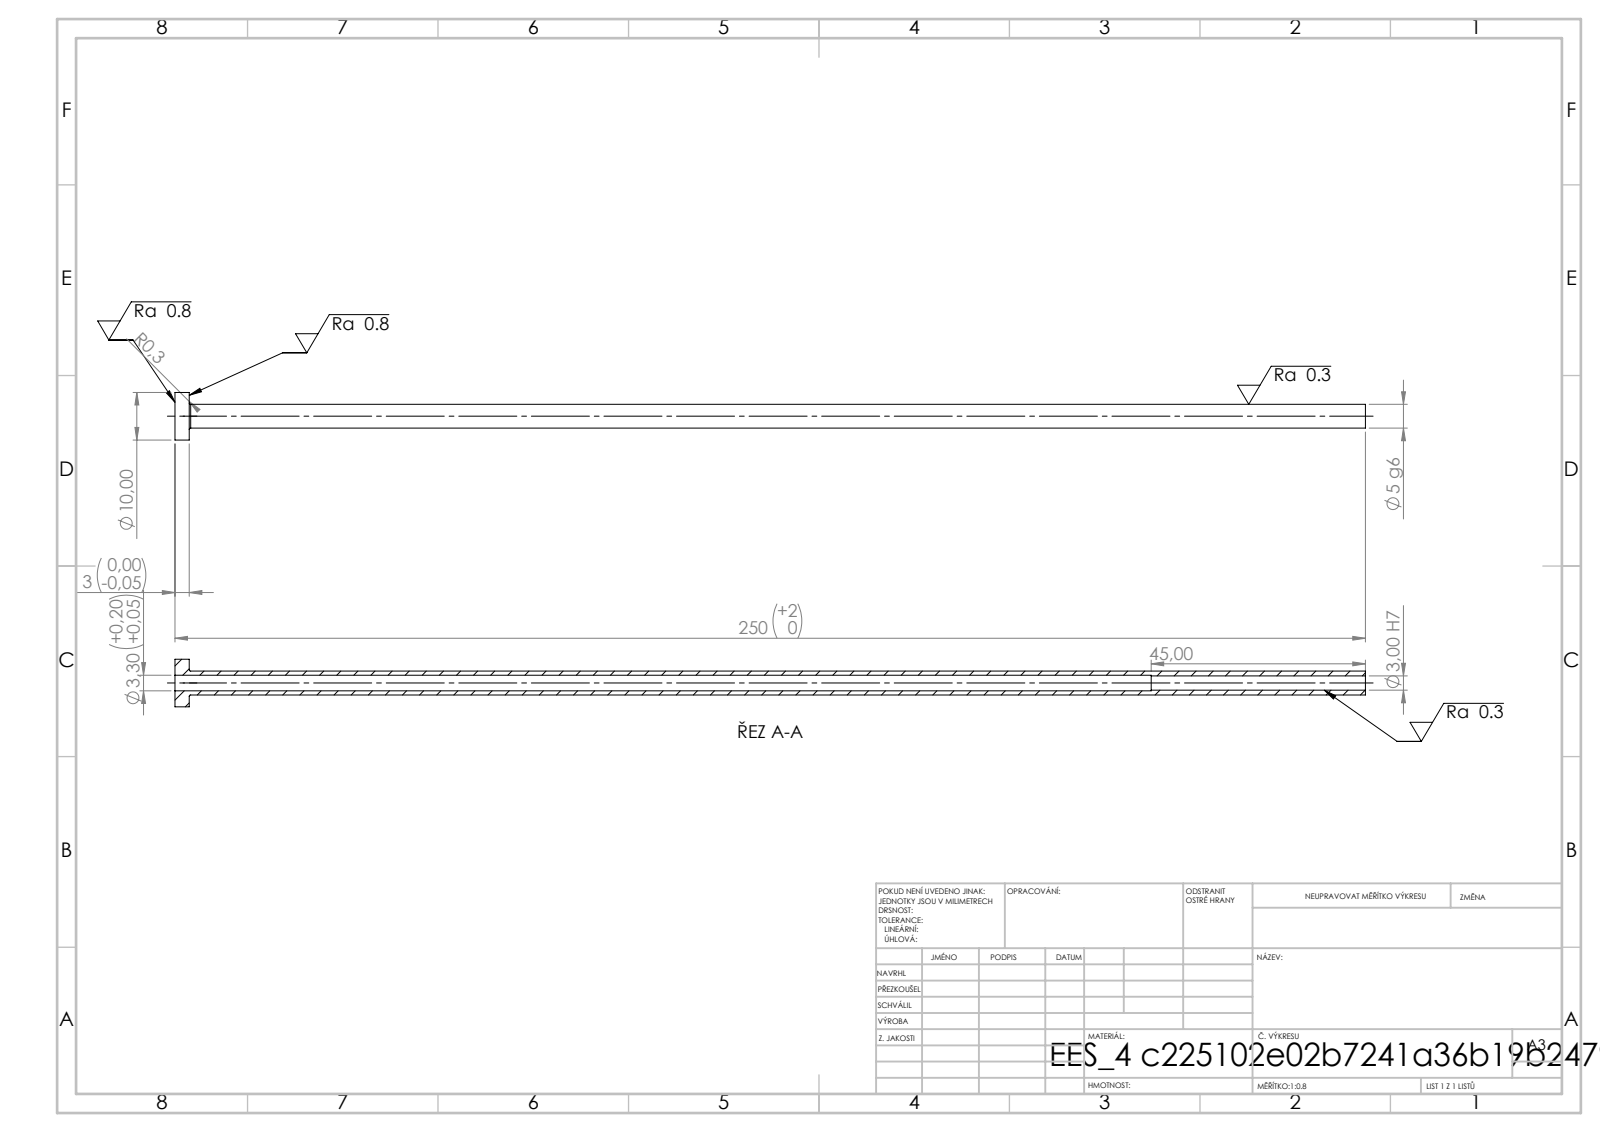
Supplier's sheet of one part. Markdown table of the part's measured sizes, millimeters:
| quantity | value |
| --- | --- |
| STEP written by | SolidWorks 2019 (CONFIG_CONTROL_DESIGN) |
| units | millimeters |
| bodies | 1 solid, 14 faces (4 planar, 8 cylindrical, 2 other) |
| overall size | 250 × 10 × 10 |
| volume | 3 014 mm³ |
| surface area | 6 664 mm² |
| round holes (diameter × count) | 3 × 1, 3.3 × 1 |
| round bosses / shafts (diameter × count) | 10 × 1, 5 × 1 |
| main face-to-face distances | 3, 250, 247, 205, 202, 45 |
